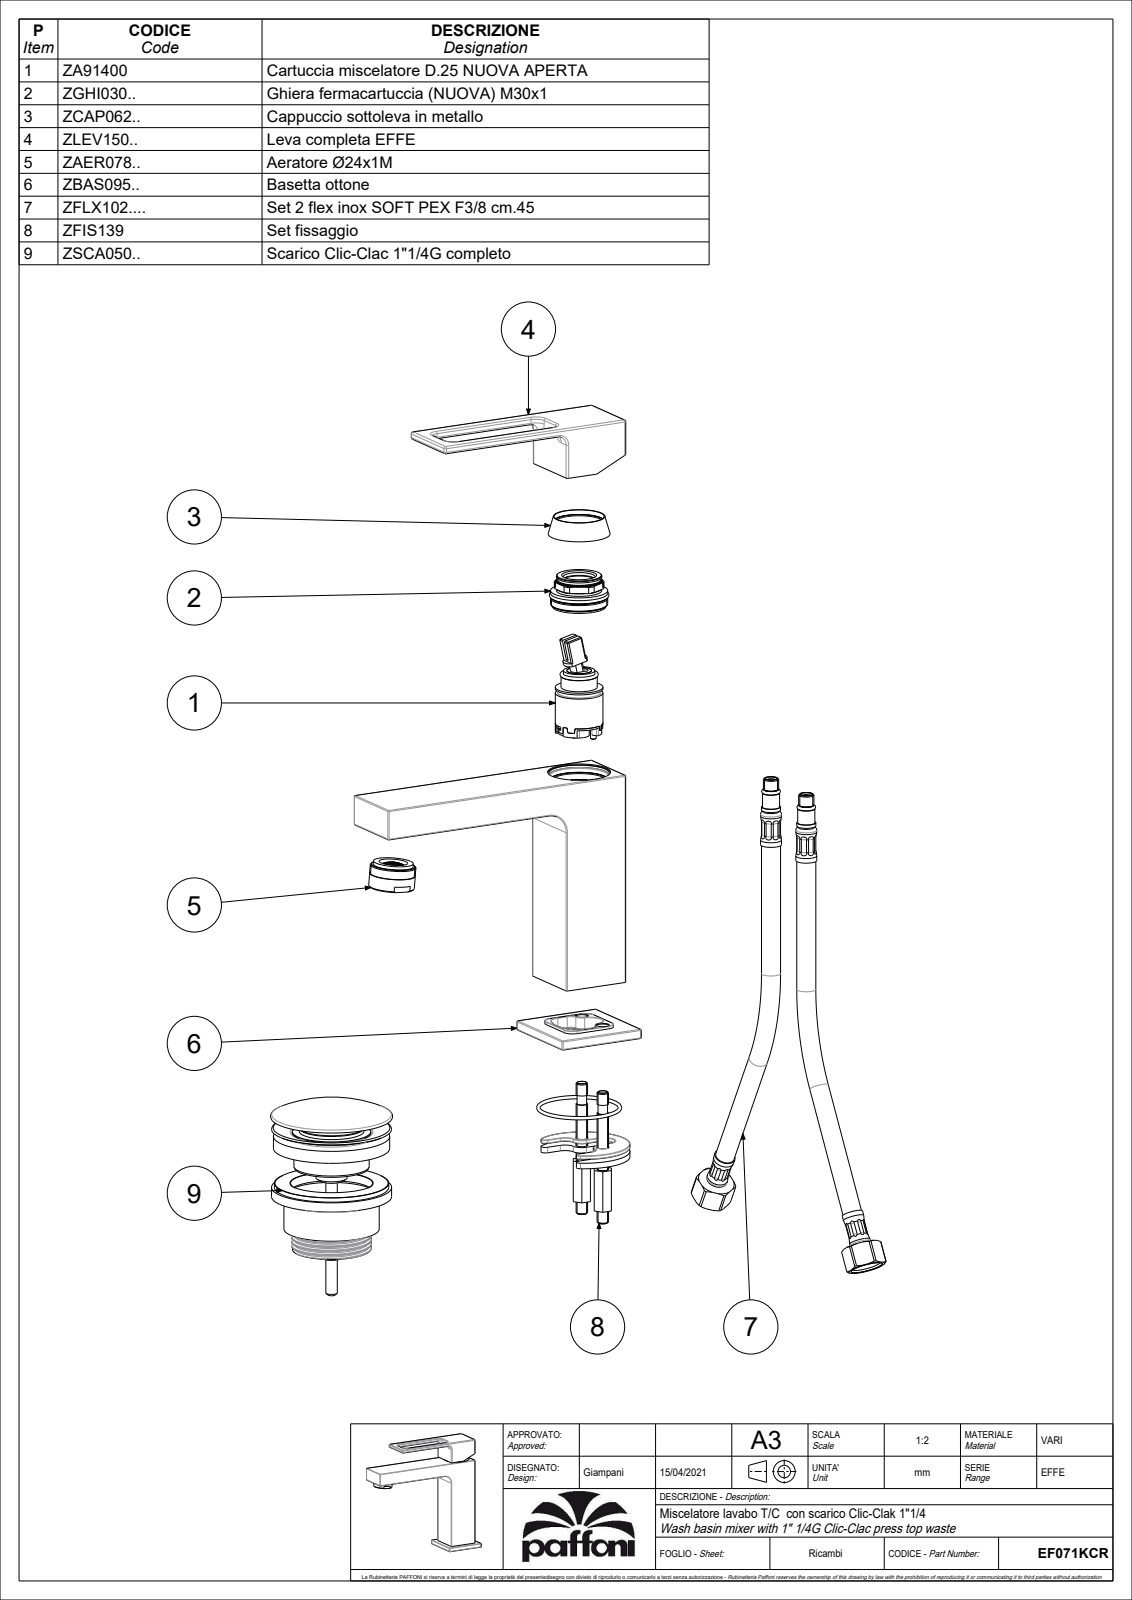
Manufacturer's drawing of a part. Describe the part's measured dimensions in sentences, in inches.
The part is named "EF071CR". Its 3-D file was written by "CREO PARAMETRIC BY PTC INC, 2020044 (CONFIG_CONTROL_DESIGN)". It is 4 solids with 1996 faces: 1556 planar, 243 cylindrical and 197 other. Overall it measures 5.906 by 5.731 by 1.89 inches. Its volume is 7.638 cubic inches and its surface area 120.3 square inches. Round holes: 3 of diameter 0.217, 2 of diameter 0.126, 2 of diameter 0.197, 2 of diameter 0.244, 2 of diameter 0.276, 2 of diameter 0.339, 2 of diameter 0.37, 1 of diameter 0.118, 1 of diameter 0.138, 1 of diameter 0.165, 1 of diameter 0.177, 1 of diameter 0.307. Round bosses or shafts: 1 of diameter 1.646, 1 of diameter 1.079, 1 of diameter 0.984, 1 of diameter 0.945, 1 of diameter 0.768, 1 of diameter 0.74, 1 of diameter 0.661, 1 of diameter 0.299. Partial cylindrical surfaces (rounded edges, fillets, slot ends): 62 of radius 0.039, 27 of radius 0.02, 11 of radius 0.197, 8 of radius 0.059, 6 of radius 0.01, 6 of radius 0.157, 2 of radius 0.138, 2 of radius 0.276. The main face-to-face distances are 0.118, 1.417, 1.299, 0.512, 1.181, 0.63, 1.106, 1.617, 1.735, 1.224. The hole center spacings are 0.618, 0.028, 0.197, 0.268, 0.274, 0.306, 0.33, 0.352.
